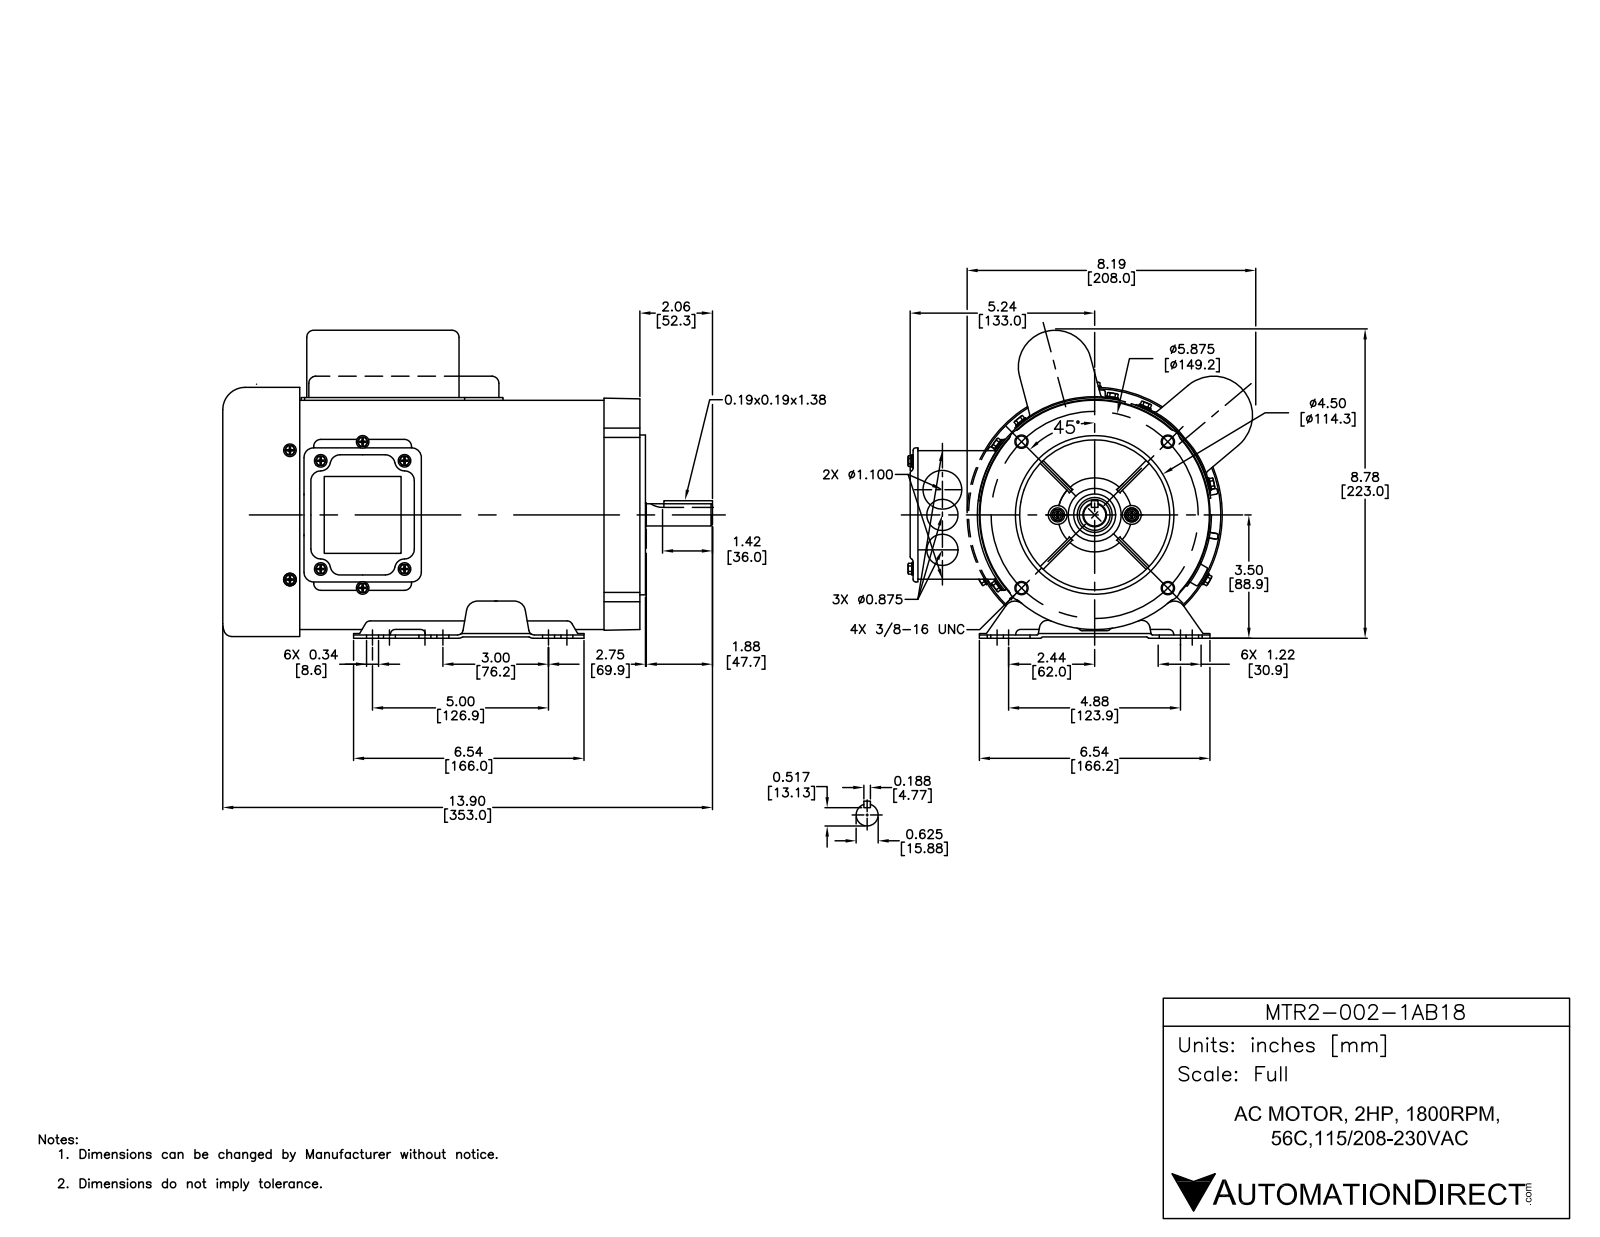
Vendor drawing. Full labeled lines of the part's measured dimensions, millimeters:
Part name (STEP PRODUCT): Tail Shaft A; Shaft Key1875 x 1875 x 1.38; Large Cap Gasket·; Front keyed shaft (+8 more)
STEP written by: SolidWorks 2015 (AUTOMOTIVE_DESIGN)
Units: millimetres
Bodies: 56 solids, 2666 faces (1010 planar, 1053 cylindrical, 603 other)
Overall size (bounding box): 353.2 × 239 × 227.7
Volume: 1 017 000 mm³ · Surface area: 883 200 mm²
Round holes (diameter × count): ⌀5.6 ×13, ⌀5 ×12, ⌀3.5 ×9, ⌀7 ×8, ⌀5.5 ×6, ⌀6.3 ×6, ⌀8.7 ×6, ⌀3.9 ×4, ⌀8 ×4, ⌀18 ×3, ⌀3.4 ×2, ⌀6.9 ×2
Round bosses / shafts (diameter × count): ⌀8.8 ×13, ⌀4.2 ×13, ⌀162.5 ×2, ⌀14 ×2, ⌀10.5 ×2, ⌀6.3 ×2, ⌀4.8 ×2, ⌀182.5 ×1
Partial cylindrical surfaces — rounded edges, fillets, slot ends (radius × count): R3 ×101, R1 ×62, R5.8 ×32, R1.9 ×23, R5 ×22, R8 ×18, R7 ×17, R2.5 ×16
Main face-to-face distances: 1, 6, 3, 1.9, 263.9, 57, 1.6, 35.3, 41.2, 34.2
Hole centre spacings: 77, 107.2, 60, 108.9, 2.4, 61.2, 97.6, 97.6
